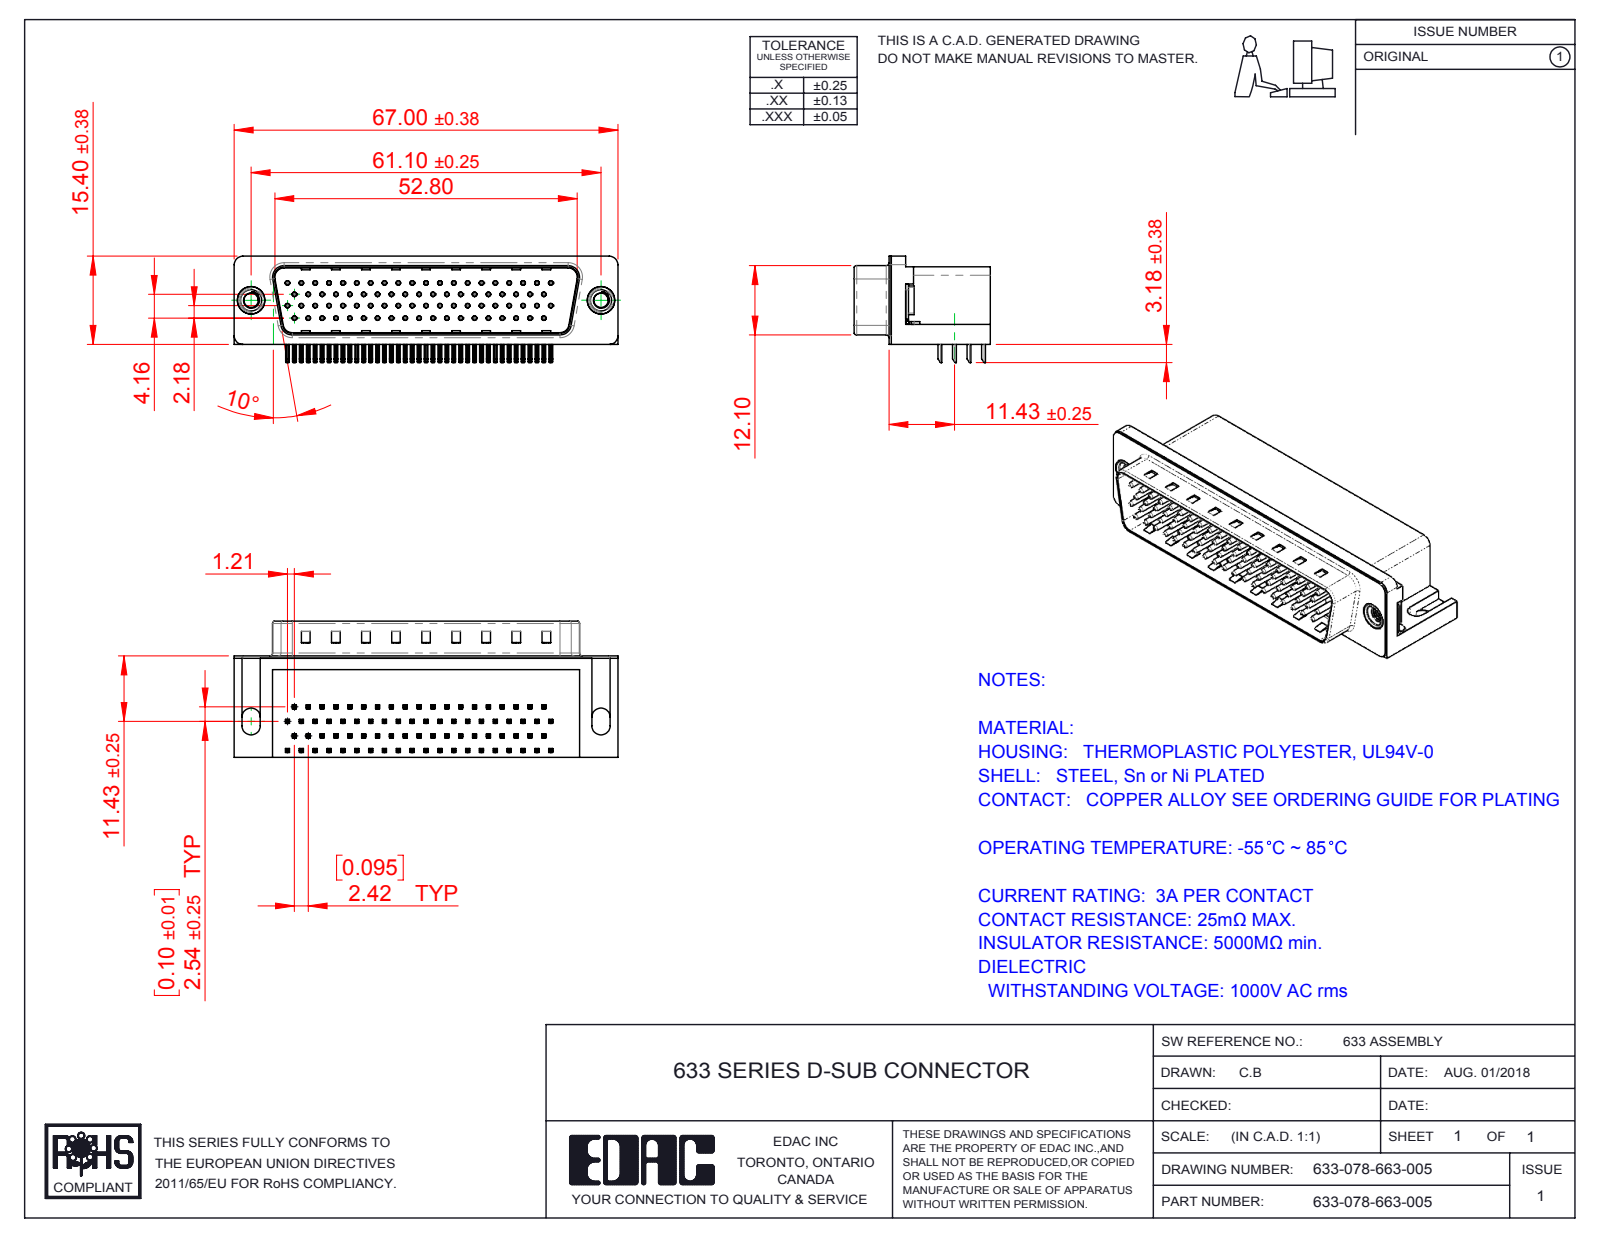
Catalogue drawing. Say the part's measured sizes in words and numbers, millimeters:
The part is named "633-078-663-005; 633 Contact Bottom_78 Contact; 633 M3 Threaded Rivet; 633 Non Board Mount_78 Contact (+5 more)". Its 3-D file was written by "SolidWorks 2016 (CONFIG_CONTROL_DESIGN)". It is 84 solids with 6270 faces: 3979 planar, 1778 cylindrical and 513 other. Overall it measures 67 by 23.8 by 18.58 millimeters. Its volume is 14 559 cubic millimeters and its surface area 16 128 square millimeters. Round holes: 78 of diameter 0.35, 78 of diameter 0.8, 2 of diameter 2.5, 2 of diameter 4, 2 of diameter 4.8, 2 of diameter 5. Round bosses or shafts: 78 of diameter 0.75, 2 of diameter 4.9, 2 of diameter 4.75, 2 of diameter 3.9. Partial cylindrical surfaces (rounded edges, fillets, slot ends): 320 of radius 0.25, 156 of radius 0.12, 16 of radius 1, 9 of radius 0.5, 8 of radius 1.6, 6 of radius 1.5, 4 of radius 0.45, 4 of radius 0.9. The main face-to-face distances are 0.4, 13.2, 17.3, 11.7, 13.35, 2.05, 13.75, 1.65, 11.9, 1.85. The hole center spacings are 2.42, 4.84, 7.26, 9.68, 6.26, 7.13, 12.1, 8.62.
